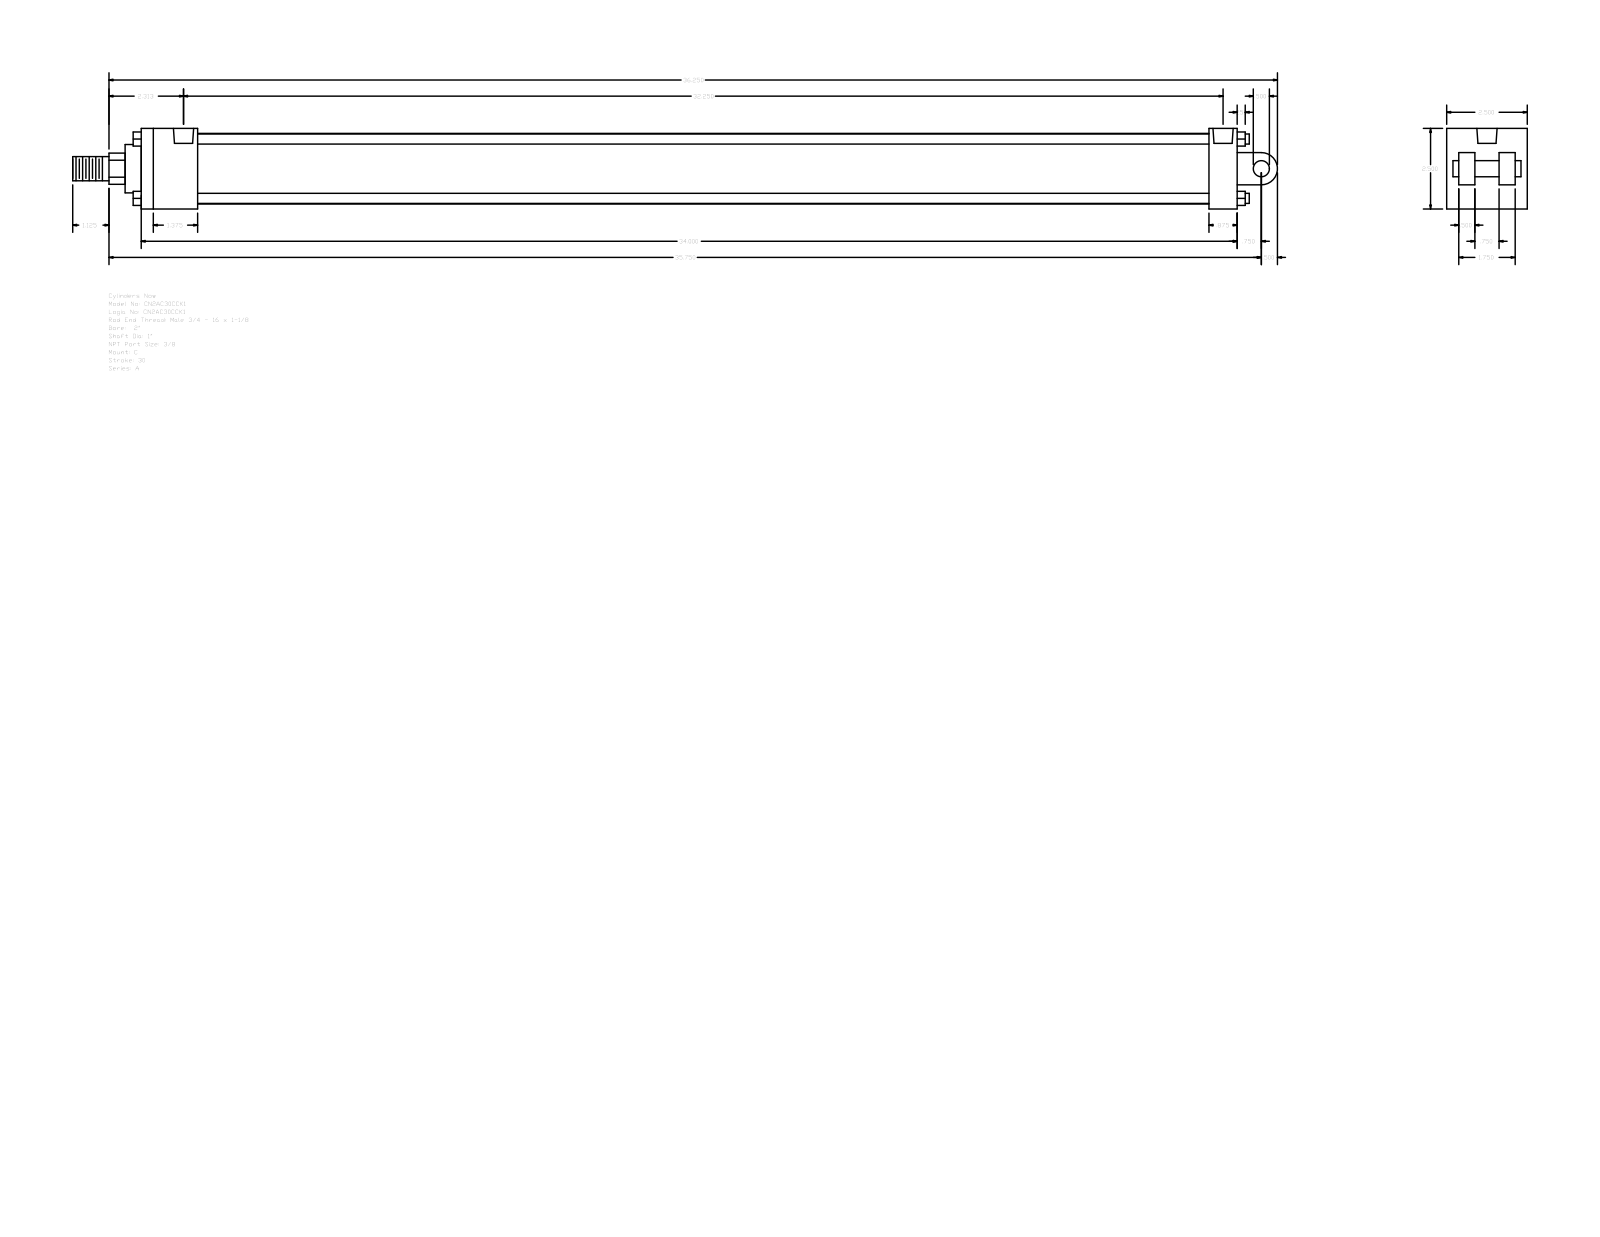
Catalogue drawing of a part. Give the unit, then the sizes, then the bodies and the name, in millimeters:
Units: millimetres
Overall size (bounding box): 949.33 × 63.5 × 63.5
Round holes (diameter × count): ⌀5.56 ×4, ⌀15.93 ×2
Round bosses / shafts (diameter × count): ⌀7.94 ×4, ⌀55.63 ×1, ⌀38.1 ×1, ⌀25.4 ×1, ⌀19.05 ×1, ⌀12.7 ×1
Partial cylindrical surfaces — rounded edges, fillets, slot ends (radius × count): R12.29 ×1, R12.7 ×1
Main face-to-face distances: 63.5, 863.6, 44.45, 12.7, 9.52, 819.15, 841.37, 796.92, 22.23, 53.98
Hole centre spacings: 813.58, 1.59, 3.98, 815.17, 817.56, 819.15
Bodies: 0 solids, 135 faces (102 planar, 33 cylindrical, 0 other)
Part name (STEP PRODUCT): A_C__0200_1
STEP written by: GSSL Pune (CONFIG_CONTROL_DESIGN)
